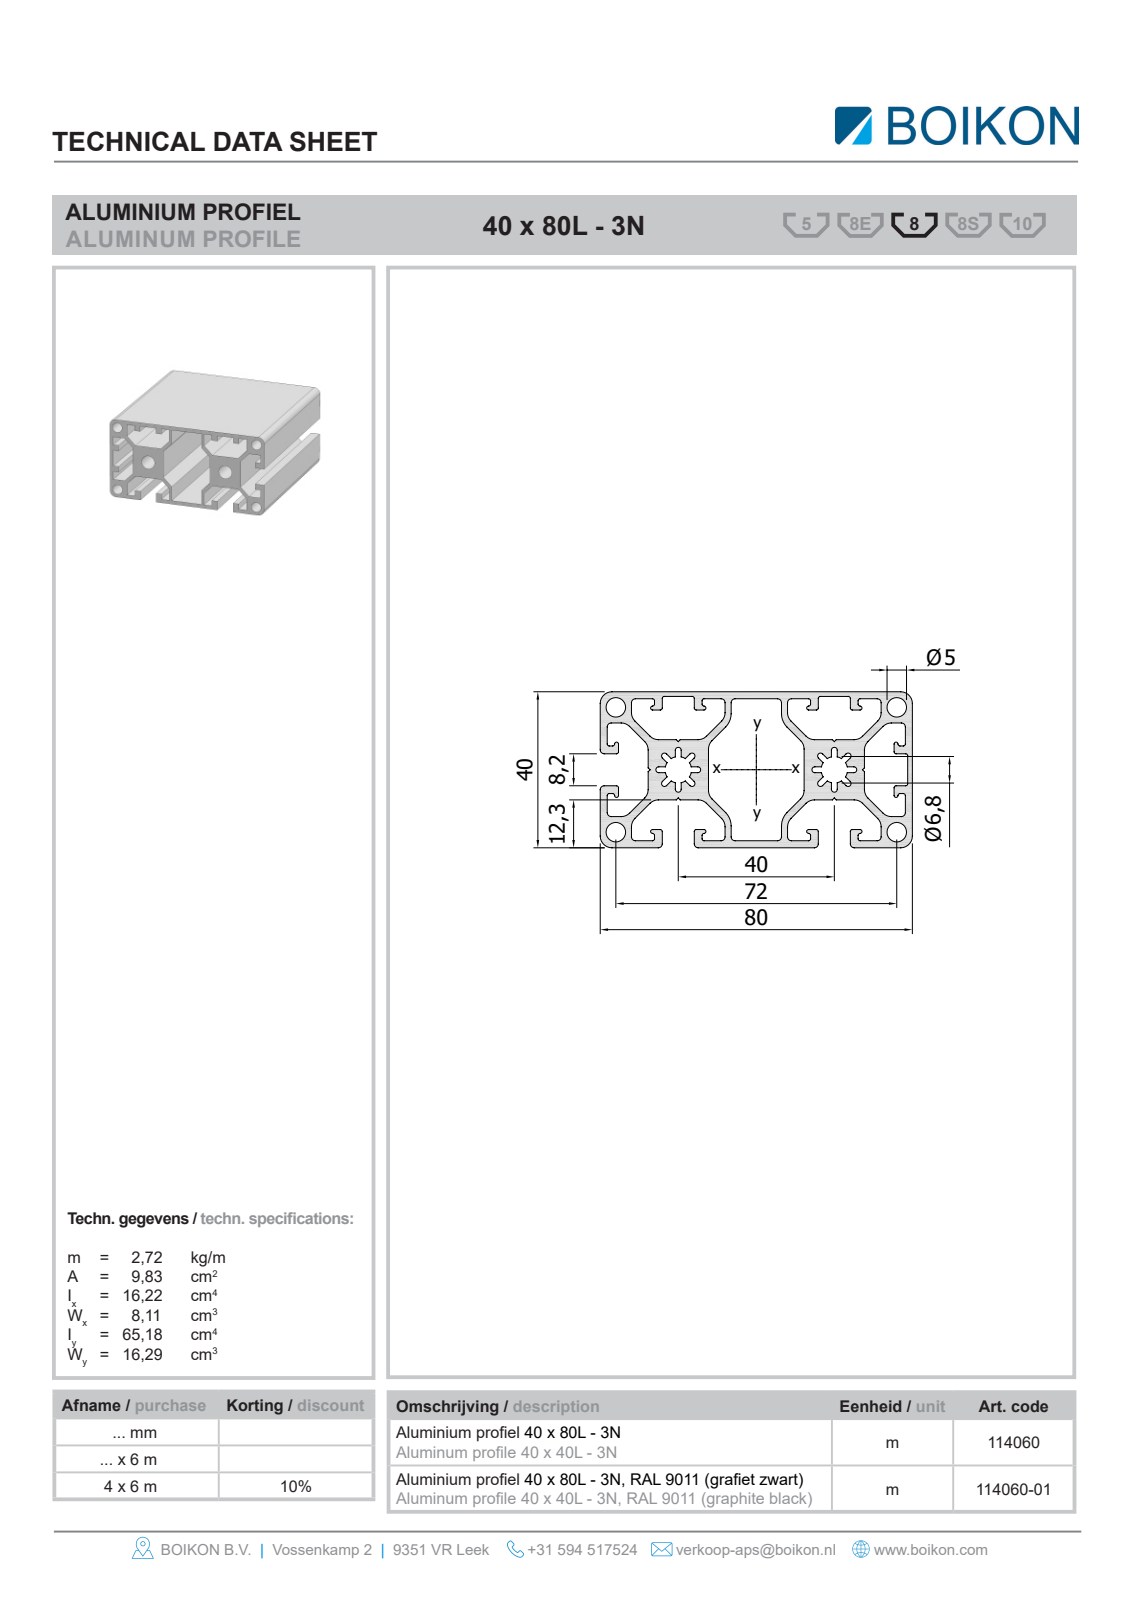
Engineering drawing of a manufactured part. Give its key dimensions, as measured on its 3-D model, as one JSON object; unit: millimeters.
{"part_name": "Root; 11406040x80L-3NBOIKON0", "step_written_by": "HiCAD 2013 1802.4 Build 509 (AUTOMOTIVE_DESIGN)", "units": "millimeters", "bodies": {"solids": 1, "faces": 112, "planar": 102, "cylindrical": 10, "other": 0}, "overall_size": [1000, 80, 40], "volume_mm3": 1126000, "surface_area_mm2": 836875, "round_holes": [[5, 4], [6.8, 2]], "partial_cylinders_radius": [[3, 4]], "face_to_face_distances": [1.8, 40, 38.2, 12.1, 27.9, 10.3, 26.1, 3.1, 18.9, 4.5], "hole_center_spacings": [22.63, 58.24, 32, 72, 78.79, 40]}
